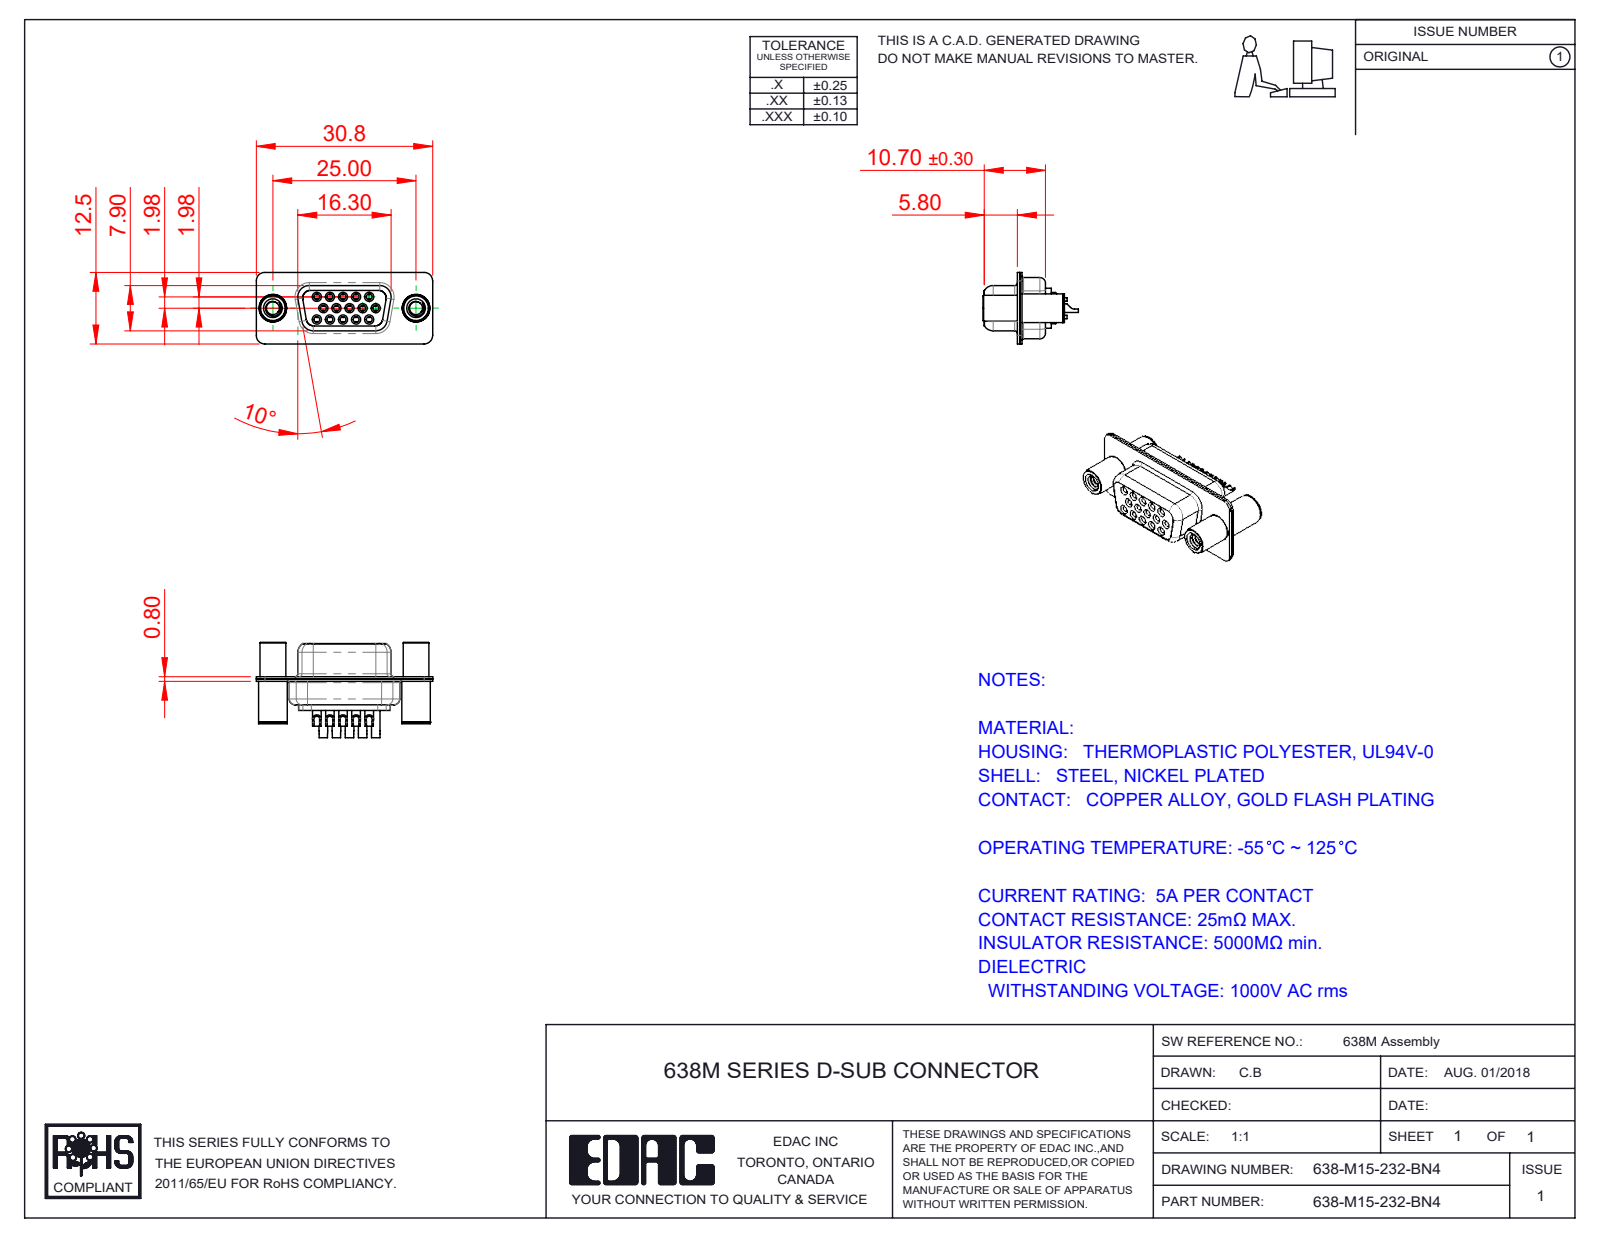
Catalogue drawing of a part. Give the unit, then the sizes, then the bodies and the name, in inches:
Units: inches
Overall size (bounding box): 1.213 × 0.656 × 0.492
Round holes (diameter × count): ⌀0.039 ×16, ⌀0.043 ×15, ⌀0.067 ×15, ⌀0.071 ×15, ⌀0.079 ×15, ⌀0.089 ×2, ⌀0.128 ×2, ⌀0.157 ×2, ⌀0.189 ×2
Round bosses / shafts (diameter × count): ⌀0.087 ×15, ⌀0.063 ×15, ⌀0.059 ×15, ⌀0.197 ×2, ⌀0.193 ×2, ⌀0.177 ×2
Partial cylindrical surfaces — rounded edges, fillets, slot ends (radius × count): R0.059 ×16, R0.079 ×12, R0.053 ×8, R0.063 ×8, R0.039 ×7, R0.01 ×4, R0.02 ×4, R0.024 ×4
Main face-to-face distances: 0.016, 0.055, 0.018, 0.333, 0.031, 0.35, 0.039, 0.071, 0.244, 0.278
Hole centre spacings: 0.09, 0.156, 0.09, 0.18, 0.238, 0.238, 0.27, 0.312
Volume: 0.119 in³ · Surface area: 9.24 in²
Bodies: 20 solids, 1190 faces (328 planar, 504 cylindrical, 358 other)
Part name (STEP PRODUCT): 638M Shell Front_15 Contacts; 638M Contact Row 2_32; 638M Housing_15 Contacts; 638M 4-40 Threaded Standoff and Board Spacer (+4 more)
STEP written by: SolidWorks 2020 (CONFIG_CONTROL_DESIGN)
